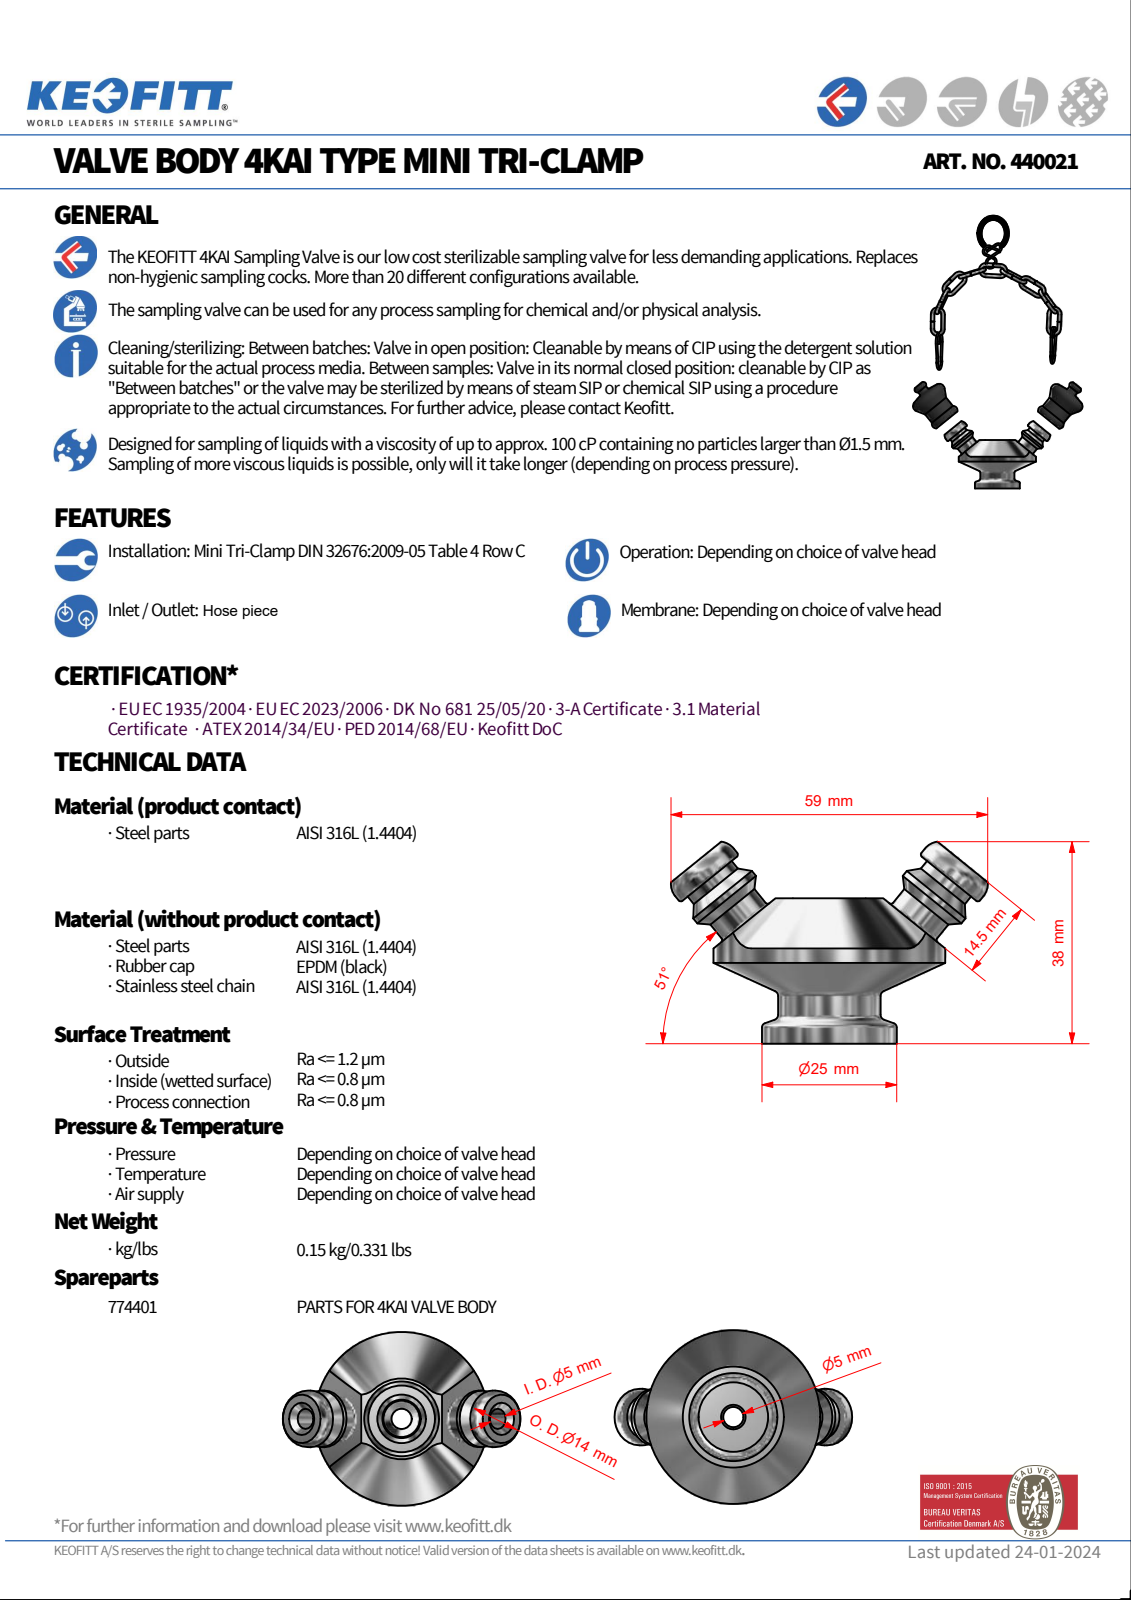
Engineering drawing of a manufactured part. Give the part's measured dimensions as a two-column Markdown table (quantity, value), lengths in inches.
| quantity | value |
| --- | --- |
| part name | 440021 |
| STEP written by | Autodesk Inventor 2020 (AUTOMOTIVE_DESIGN) |
| units | inches |
| bodies | 1 solid, 57 faces (11 planar, 23 cylindrical, 23 other) |
| overall size | 2.315 × 1.693 × 1.477 |
| volume | 1.32 in³ |
| surface area | 11.2 in² |
| round holes (diameter × count) | 0.197 × 3, 0.728 × 1, 0.858 × 1 |
| round bosses / shafts (diameter × count) | 0.551 × 2, 0.413 × 2, 1.693 × 1, 0.984 × 1, 0.748 × 1, 0.686 × 1 |
| partial cylindrical surfaces (radius × count) | 0.315 × 4 |
| main face-to-face distances | 1.027, 0.57, 0.031, 1.059, 0.413, 0.157, 1.063, 1.031, 0.057, 0.025 |
